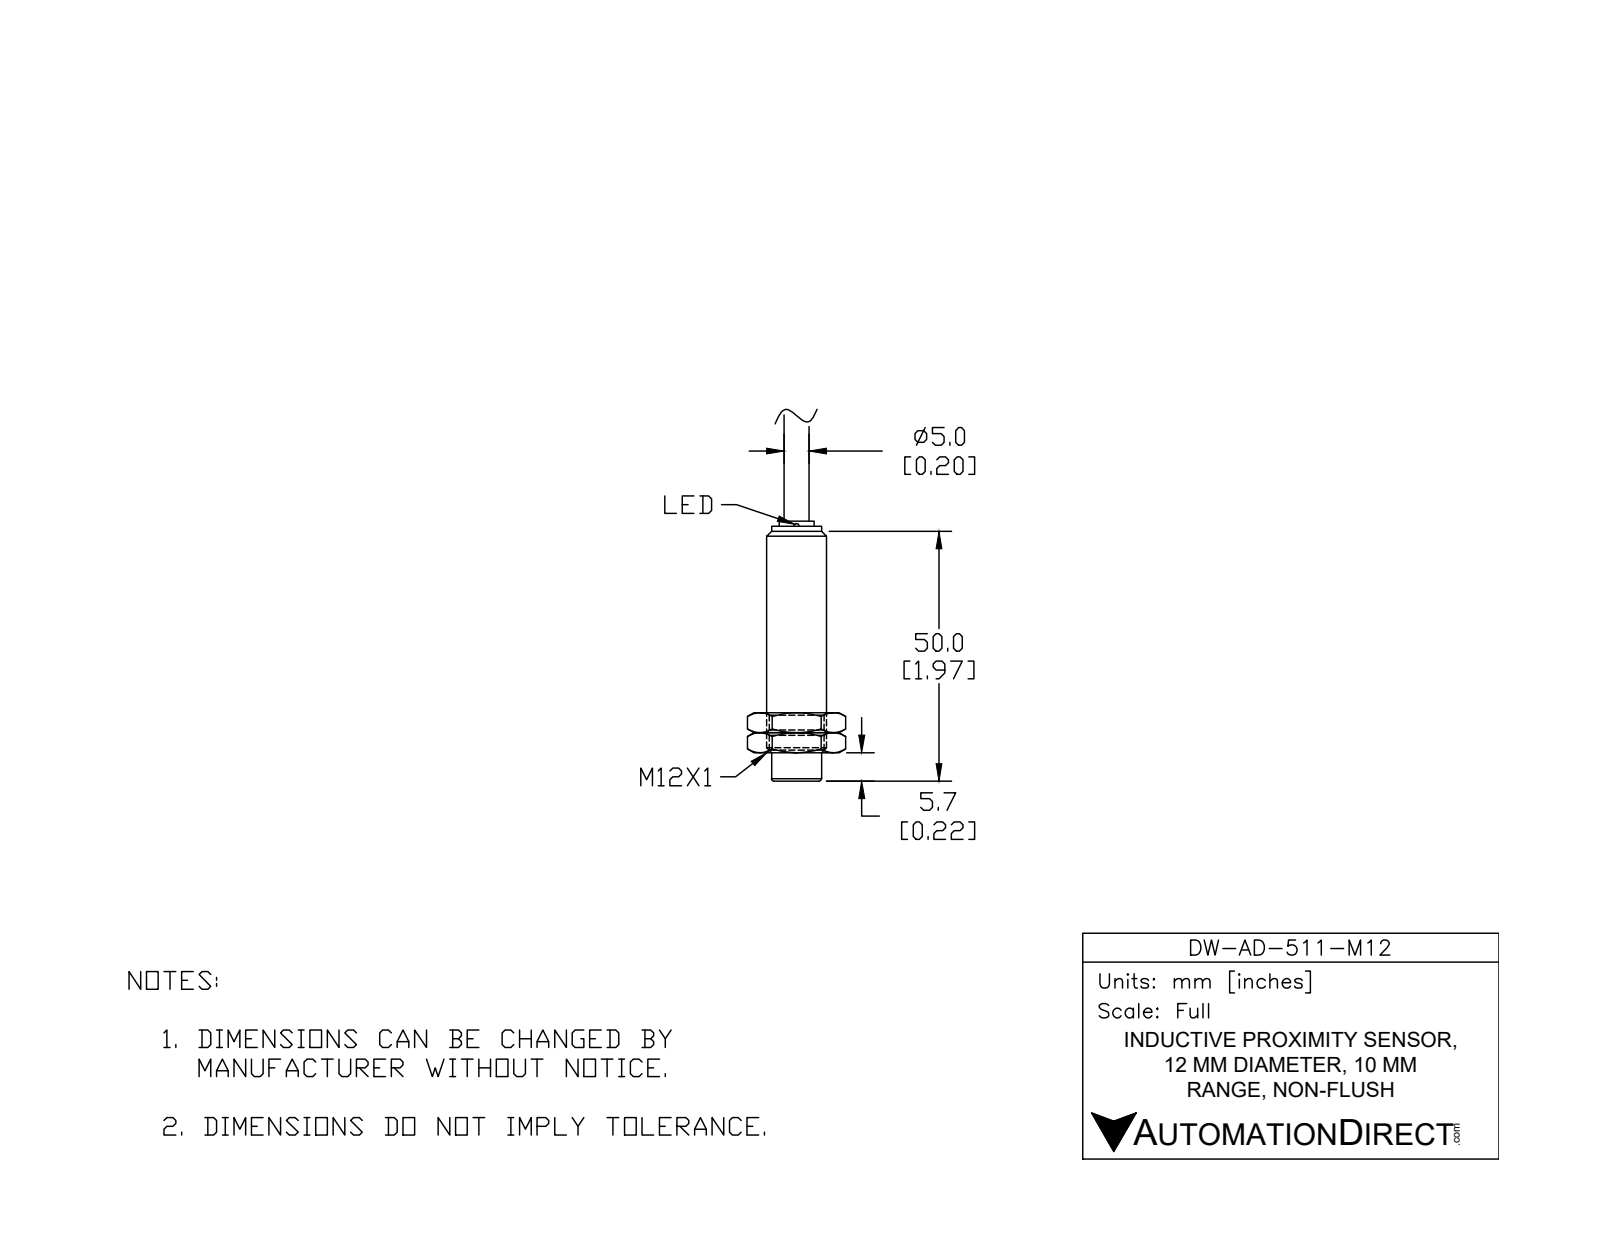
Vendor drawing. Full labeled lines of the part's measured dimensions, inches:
Part name (STEP PRODUCT): DW-AD-511-M12
STEP written by: SolidWorks 2017 (AUTOMOTIVE_DESIGN)
Units: inches
Bodies: 1 solid, 31 faces (15 planar, 5 cylindrical, 11 other)
Overall size (bounding box): 2.976 × 0.472 × 0.472
Volume: 0.37 in³ · Surface area: 3.819 in²
Round bosses / shafts (diameter × count): ⌀0.472 ×1, ⌀0.421 ×1, ⌀0.413 ×1, ⌀0.268 ×1, ⌀0.197 ×1
Main face-to-face distances: 2, 2.047, 0.047, 2.031, 0.031, 0.016
